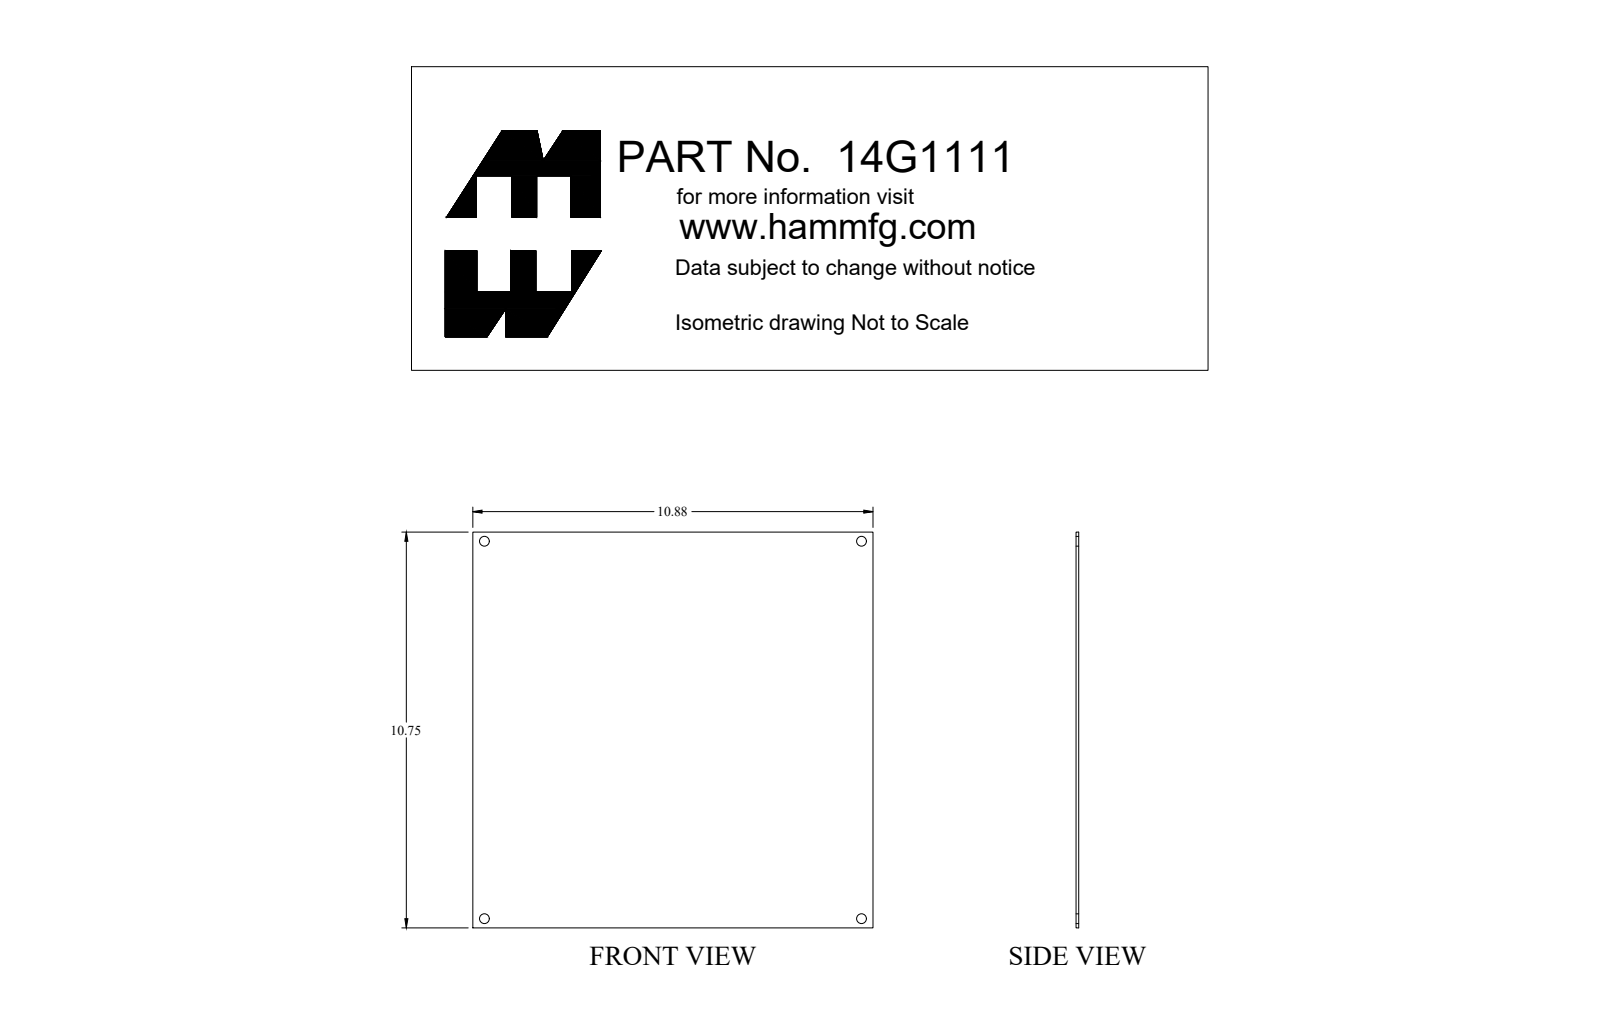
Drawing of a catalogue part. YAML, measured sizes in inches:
part_name: "14G1111"
step_written_by: "SolidWorks 2018 (AUTOMOTIVE_DESIGN)"
units: inches
bodies: {solids: 1, faces: 10, planar: 6, cylindrical: 4, other: 0}
overall_size: [10.875, 10.75, 0.072]
volume: 8.401
surface_area: 236.7
round_holes:
  - {diameter: 0.265, count: 4}
face_to_face_distances: [0.072, 10.75, 10.875]
hole_center_spacings: [10.25, 14.496]
